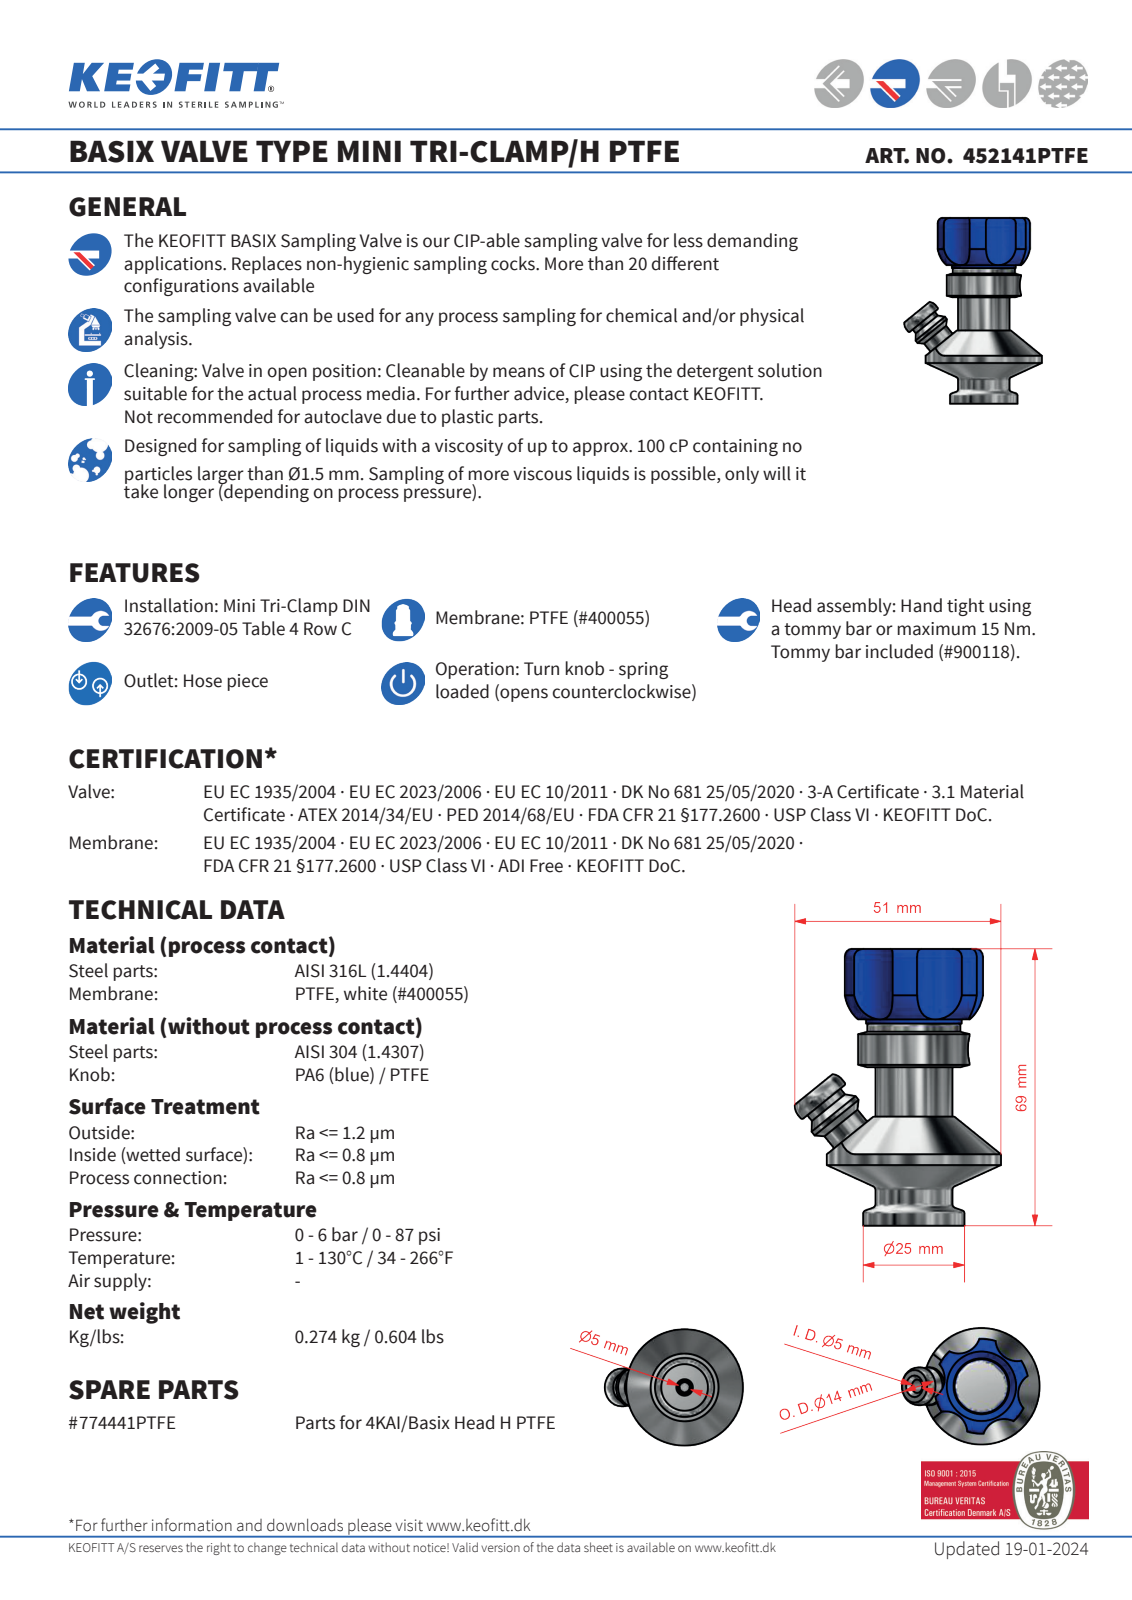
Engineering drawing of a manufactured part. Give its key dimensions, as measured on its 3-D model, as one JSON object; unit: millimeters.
{"part_name": "452141PTFE", "step_written_by": "Autodesk Inventor 2020 (AUTOMOTIVE_DESIGN)", "units": "millimeters", "bodies": {"solids": 1, "faces": 161, "planar": 48, "cylindrical": 62, "other": 51}, "overall_size": [68.5, 50.9, 43], "volume_mm3": 41262, "surface_area_mm2": 14264, "round_holes": [[5, 1], [6.05, 1], [7.3, 1], [14.2, 1], [16.5, 1], [18.5, 1], [18.6, 1], [19.6, 1], [20.6, 1], [21.8, 1]], "round_bosses_or_shafts": [[14, 2], [10.5, 2], [43, 1], [27.5, 1], [25, 1], [23.6, 1], [23, 1], [20, 1]], "partial_cylinders_radius": [[1.5, 8], [8, 8], [5.4, 1], [17.5, 1]], "face_to_face_distances": [18, 0.5, 2.5, 49.2, 67.2, 18.5, 50.24, 1.04, 16.96, 67.7]}
